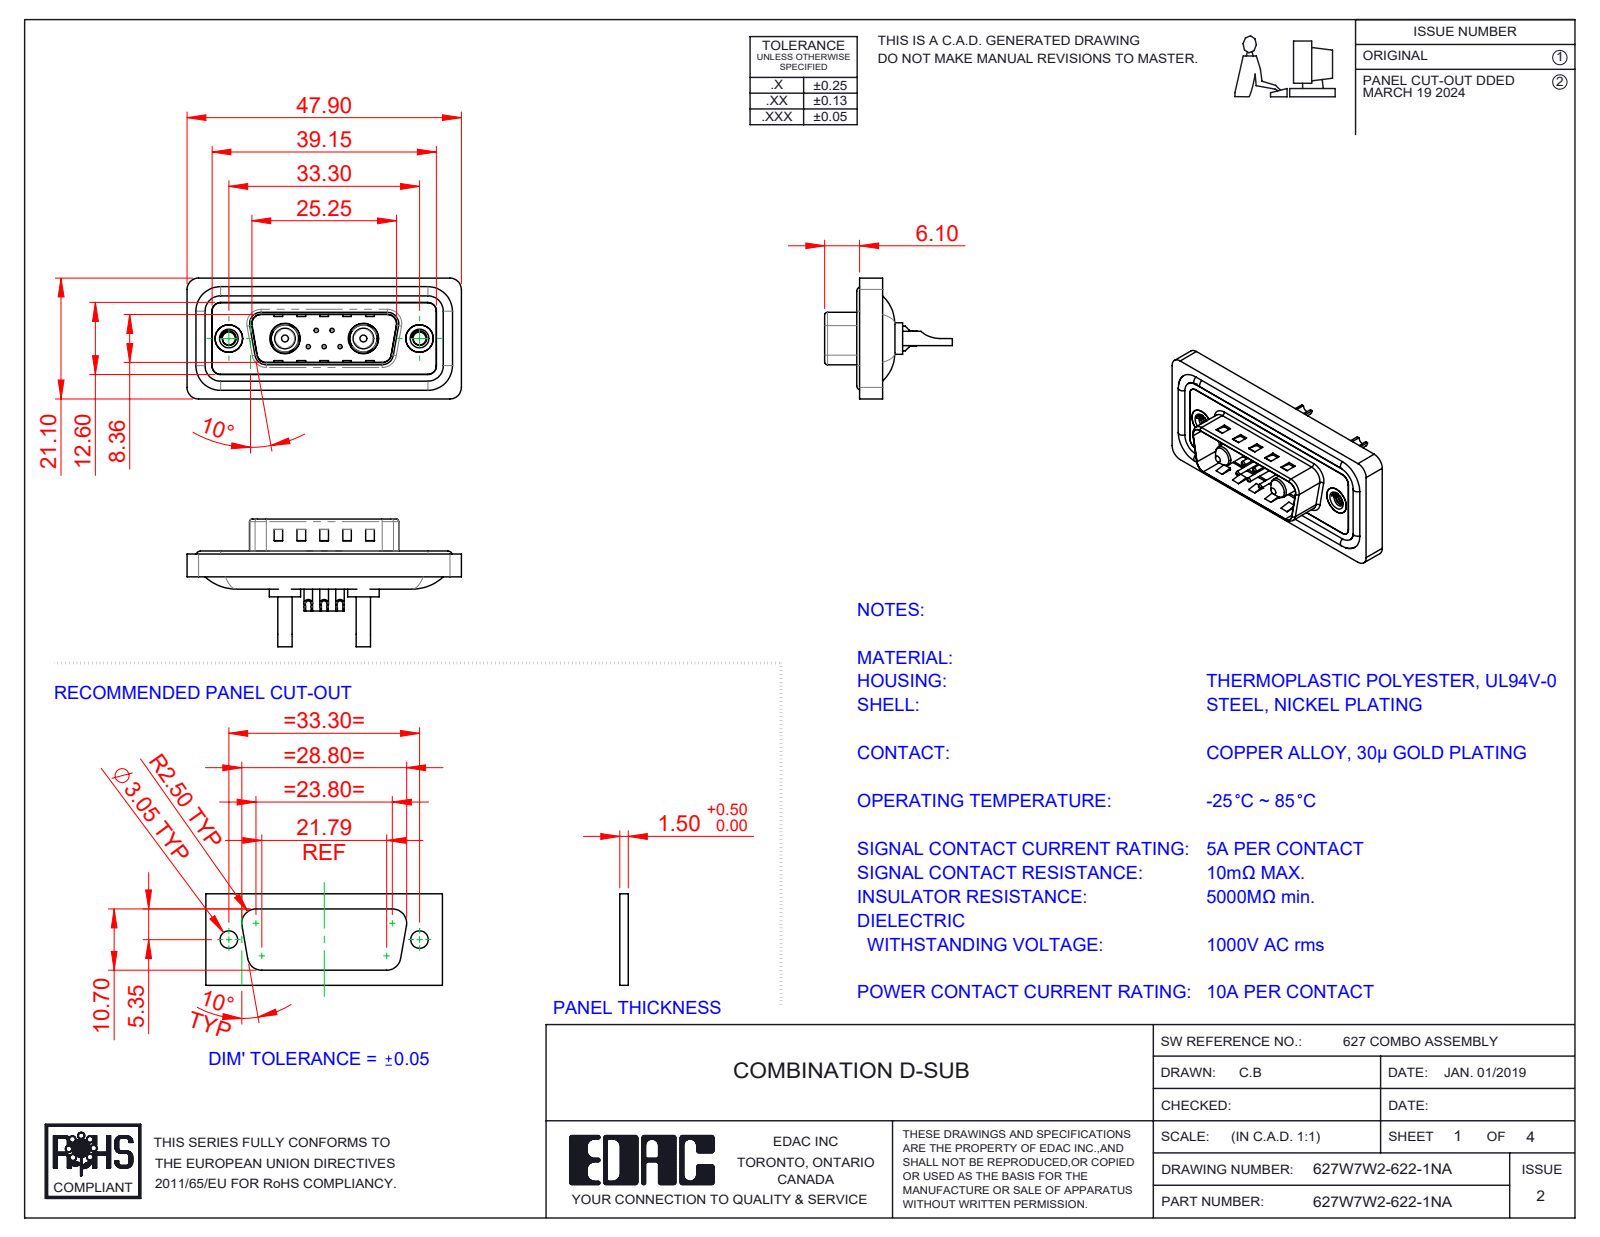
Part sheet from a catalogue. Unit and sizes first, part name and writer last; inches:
Units: inches
Overall size (bounding box): 1.886 × 0.878 × 0.831
Round holes (diameter × count): ⌀0.03 ×5, ⌀0.039 ×5, ⌀0.063 ×5, ⌀0.079 ×5, ⌀0.067 ×2, ⌀0.089 ×2, ⌀0.157 ×2, ⌀0.189 ×2, ⌀0.191 ×2, ⌀0.197 ×2, ⌀0.209 ×2
Round bosses / shafts (diameter × count): ⌀0.059 ×5, ⌀0.063 ×4, ⌀0.217 ×2, ⌀0.205 ×2, ⌀0.193 ×2, ⌀0.187 ×2, ⌀0.148 ×2, ⌀0.142 ×2
Partial cylindrical surfaces — rounded edges, fillets, slot ends (radius × count): R0.059 ×26, R0.079 ×20, R0.02 ×8, R0.063 ×8, R0.039 ×6, R0.01 ×4, R0.024 ×4, R0.026 ×4
Main face-to-face distances: 0.016, 0.043, 0.059, 0.063, 0.02, 0.122, 0.114, 0.157, 0.032, 0.377
Hole centre spacings: 0.124, 0.109, 0.386, 0.925, 0.17, 0.17, 0.198, 0.198
Volume: 0.337 in³ · Surface area: 13.84 in²
Bodies: 16 solids, 720 faces (246 planar, 310 cylindrical, 164 other)
Part name (STEP PRODUCT): 627Combo Shell Rear_15 Contacts; 627Combo Waterproof Housing_15 Contacts; 627Combo Contact Row 2_22; Power Pin_10A SC (+5 more)
STEP written by: SolidWorks 2023 (CONFIG_CONTROL_DESIGN)
